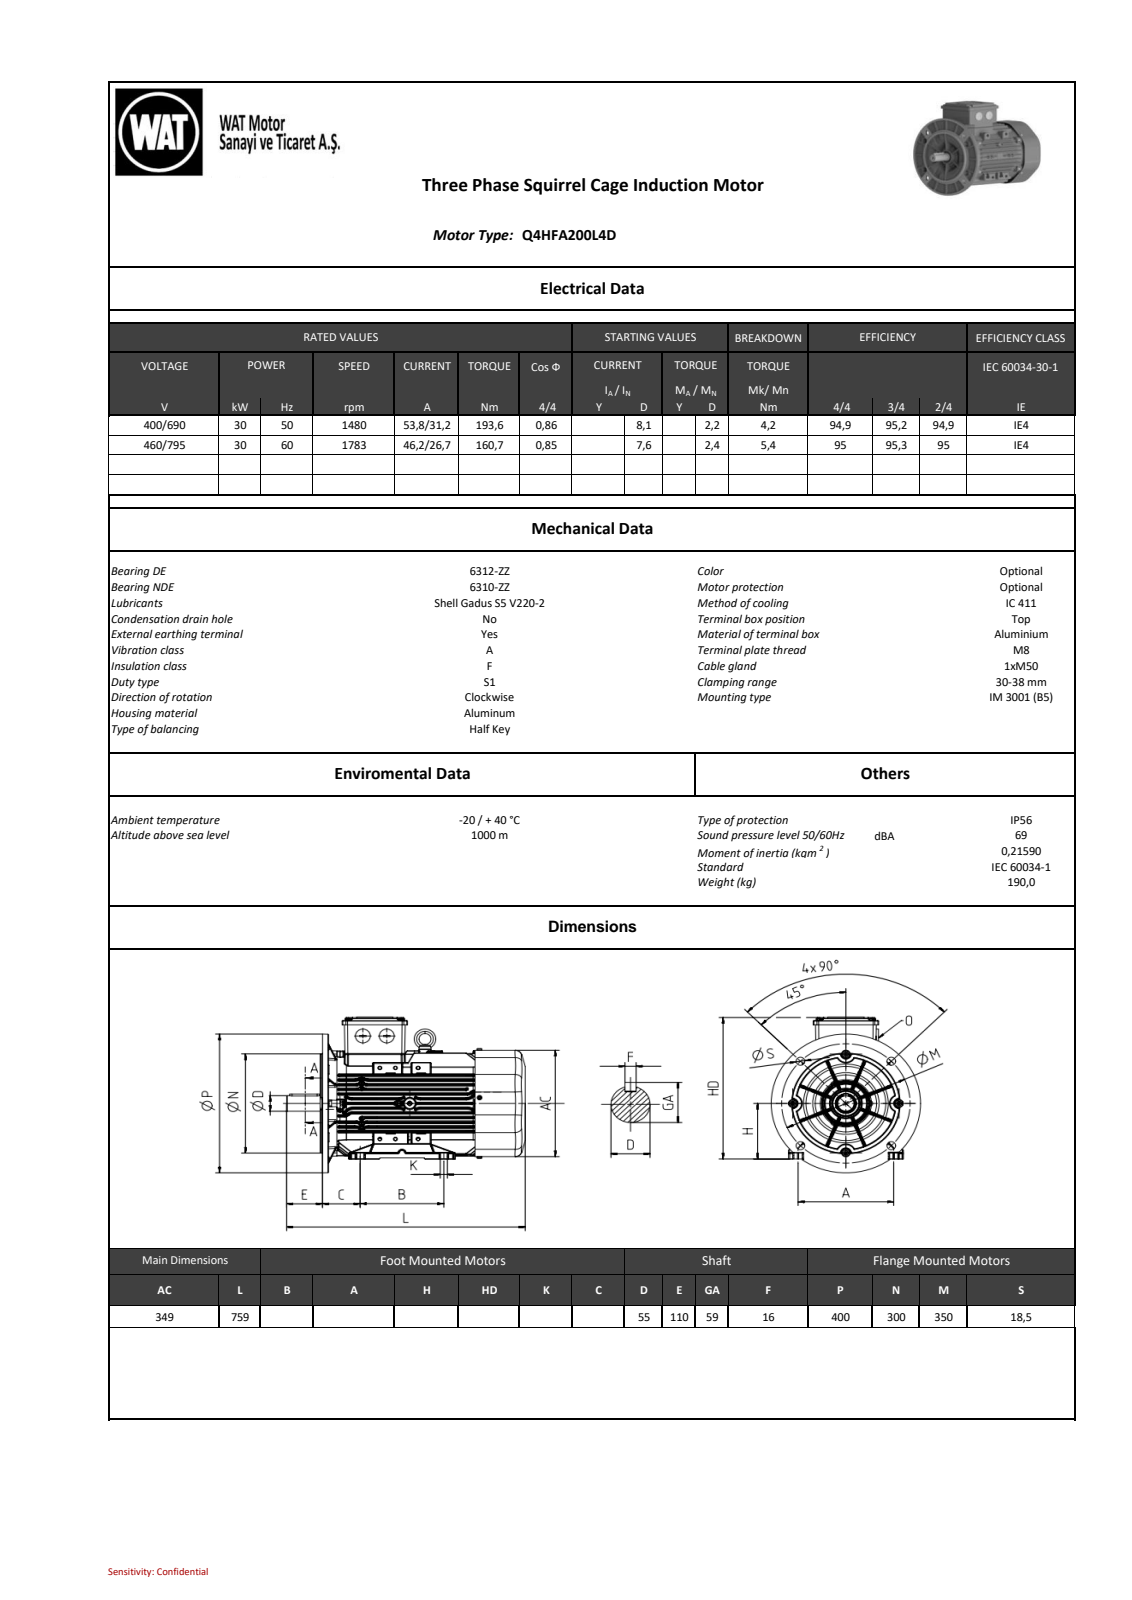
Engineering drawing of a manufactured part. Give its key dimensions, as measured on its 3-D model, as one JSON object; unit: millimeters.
{"part_name": "model1_objects", "step_written_by": "SIEMENS PLM Software NX2206.8101 (AUTOMOTIVE_DESIGN)", "units": "millimeters", "bodies": {"solids": 0, "faces": 13440, "planar": 3583, "cylindrical": 5362, "other": 4495}, "overall_size": [705.5, 451.84, 399.69], "round_holes": [[5.6, 8], [0.4, 4], [4.3, 4], [6.5, 4], [8.3, 4], [9, 4], [18.5, 4], [4, 3], [5.5, 3], [3.2, 2], [9.44, 2], [22, 2]], "round_bosses_or_shafts": [[12, 8], [5.49, 8], [4.92, 8], [8, 5], [14.8, 4], [13, 4], [9.5, 4], [6, 4]], "partial_cylinders_radius": [[0.5, 1730], [1, 798], [2, 747], [5, 275], [1.5, 172], [0.1, 122], [0.75, 99], [0.45, 48]], "face_to_face_distances": [1.2, 16.21, 6, 32.48, 16.27, 3, 171.05, 173.83, 141.35, 157.62], "hole_center_spacings": [129.23, 310.46, 136, 78.16, 169.96, 156, 161, 174.99]}
